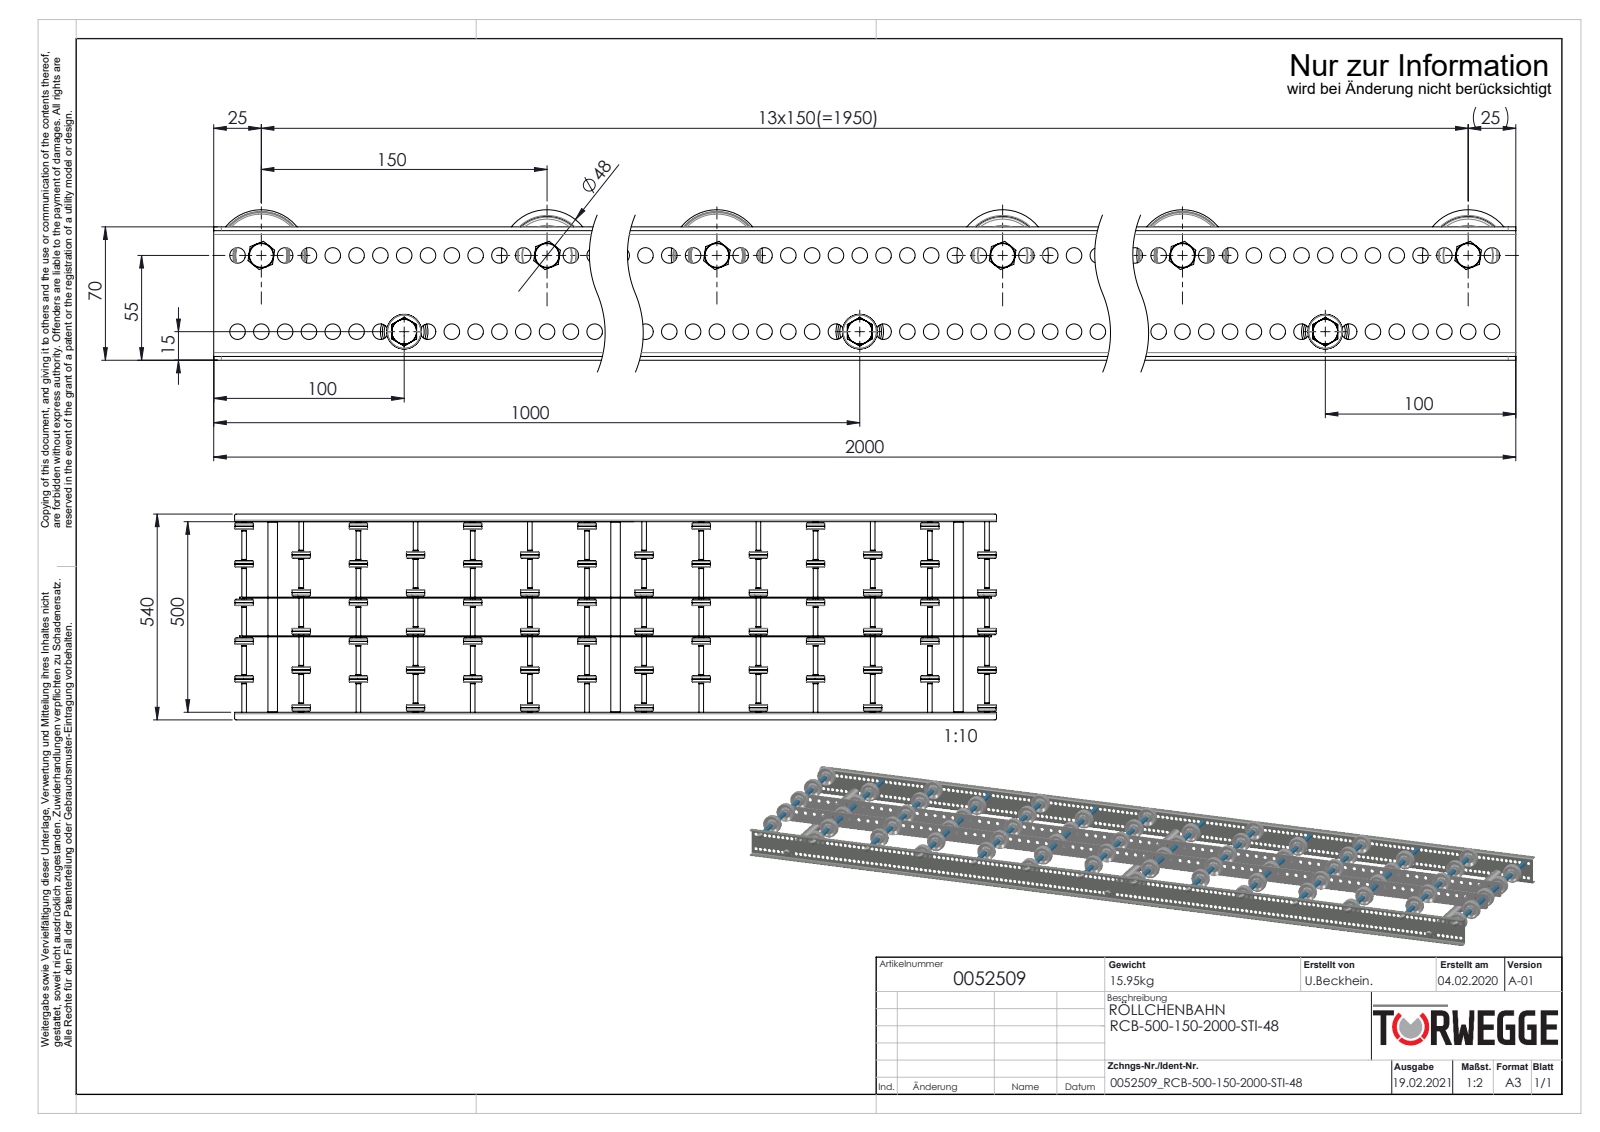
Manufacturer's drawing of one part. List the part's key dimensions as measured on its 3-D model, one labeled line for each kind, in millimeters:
Part name (STEP PRODUCT): Profil_LRB-20x70x20x2_KFG_S100202_U-PROFIL-20-70-20-2-LRB-L=2000; Traversen_KFG_L500; S106837_Gewindestange-M8-KFG_L520; S100994_Sperrzahnschraube_M08x16-8.8-A2K (+6 more)
STEP written by: SolidWorks 2020 (AUTOMOTIVE_DESIGN)
Units: millimetres
Bodies: 271 solids, 8918 faces (1686 planar, 3912 cylindrical, 3320 other)
Overall size (bounding box): 2000 × 540 × 79
Volume: 3 482 000 mm³ · Surface area: 2 819 000 mm²
Round holes (diameter × count): ⌀8.2 ×318, ⌀8.5 ×79, ⌀6.65 ×14, ⌀8 ×14, ⌀9.65 ×14, ⌀15 ×14, ⌀41 ×14, ⌀6.8 ×3, ⌀21 ×3
Round bosses / shafts (diameter × count): ⌀48 ×14, ⌀13 ×14, ⌀12.5 ×14, ⌀12.4 ×14, ⌀12 ×14, ⌀11.5 ×14, ⌀25 ×3, ⌀8 ×3
Partial cylindrical surfaces — rounded edges, fillets, slot ends (radius × count): R4 ×8, R2 ×4, R5 ×4
Main face-to-face distances: 2, 101.5, 200.5, 302, 502, 99, 200, 202.5, 301.5, 304
Hole centre spacings: 12.5, 25, 37.5, 50, 62.5, 75, 87.5, 100
